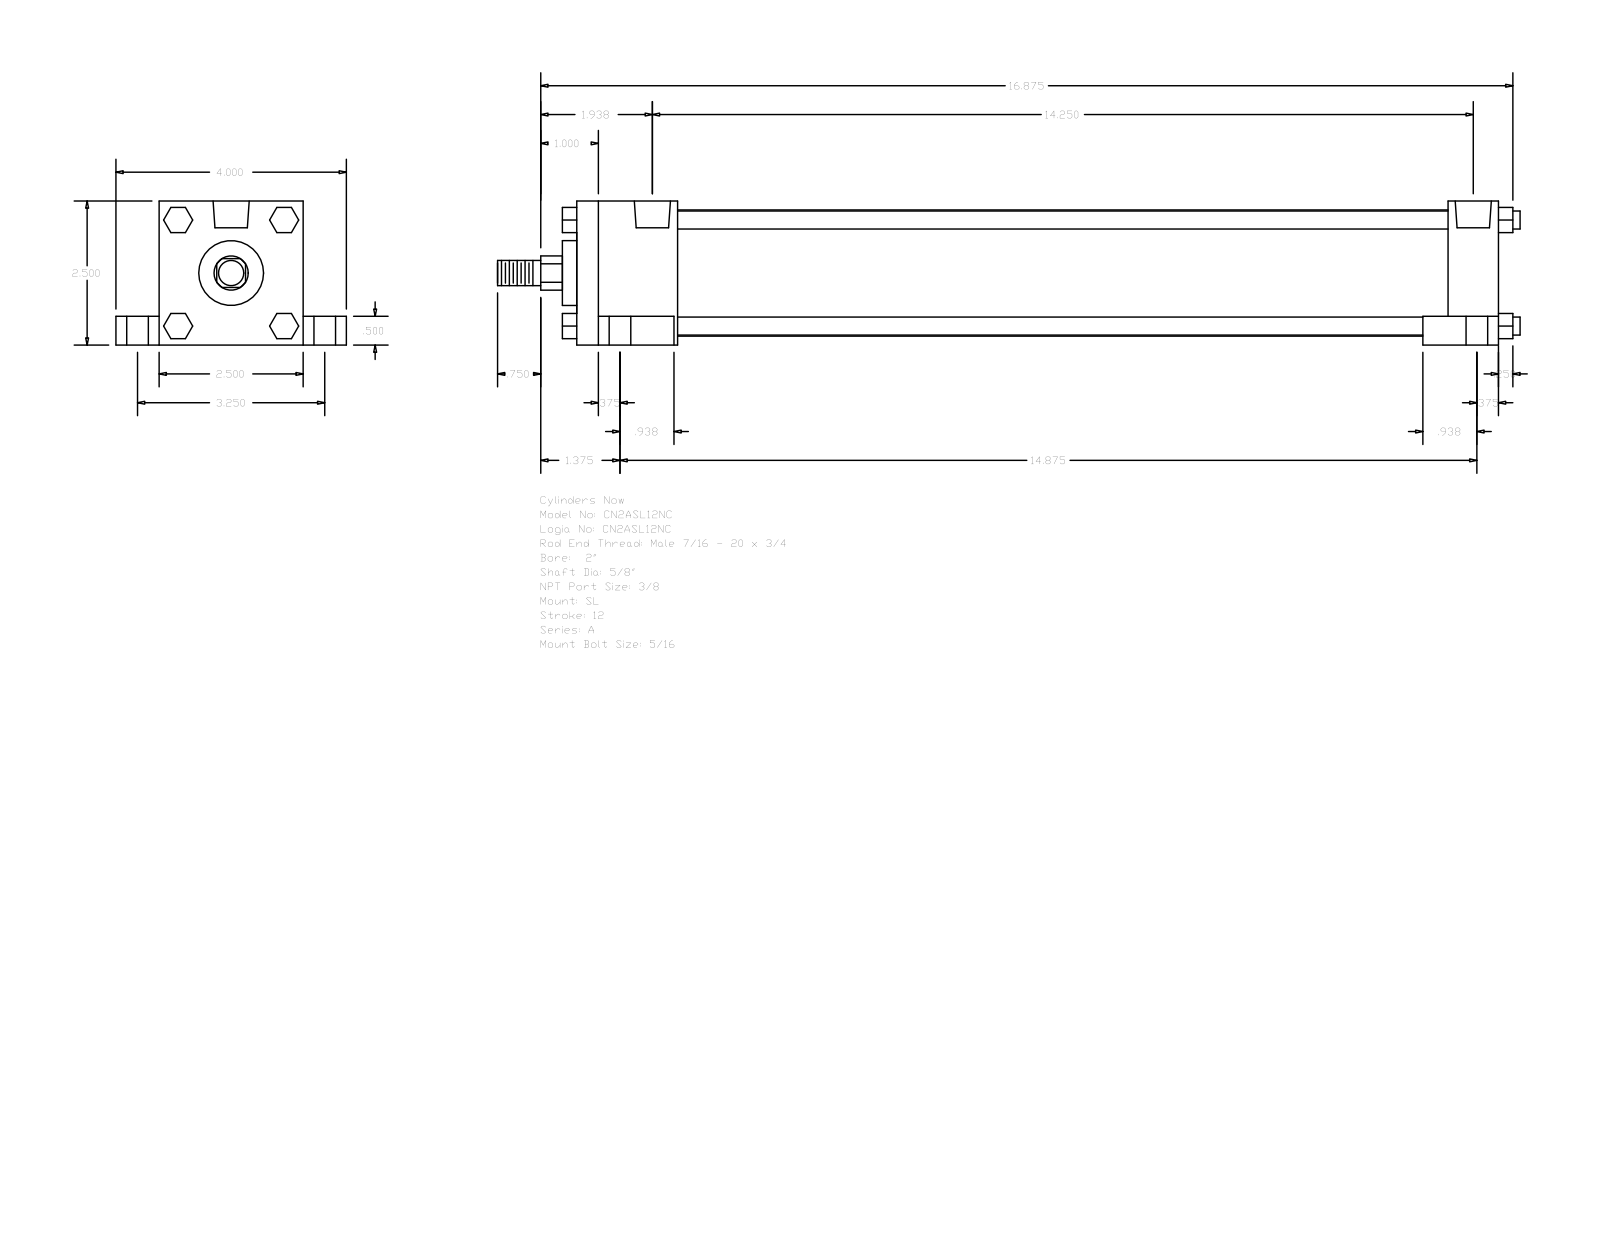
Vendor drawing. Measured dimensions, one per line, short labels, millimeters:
name: A_SL__0200_0.625
written by: GSSL Pune (CONFIG_CONTROL_DESIGN)
unit: mm
bodies: 0 solids, 148 faces (112 planar, 36 cylindrical, 0 other)
size: 450.85 × 101.6 × 63.5
holes: 4× ⌀5.56, 4× ⌀9.53, 4× ⌀15.88, 2× ⌀15.93
bosses: 4× ⌀7.94, 1× ⌀55.63, 1× ⌀28.57, 1× ⌀15.88, 1× ⌀11.11
rounds: 1× R7.54
face distances: 63.5, 406.39, 50.8, 12.7, 19.05, 82.55, 44.45, 361.94, 384.17, 339.72
hole spacings: 41.3, 41.64, 43.67, 45.13, 82.54, 354, 361.92, 365.88
